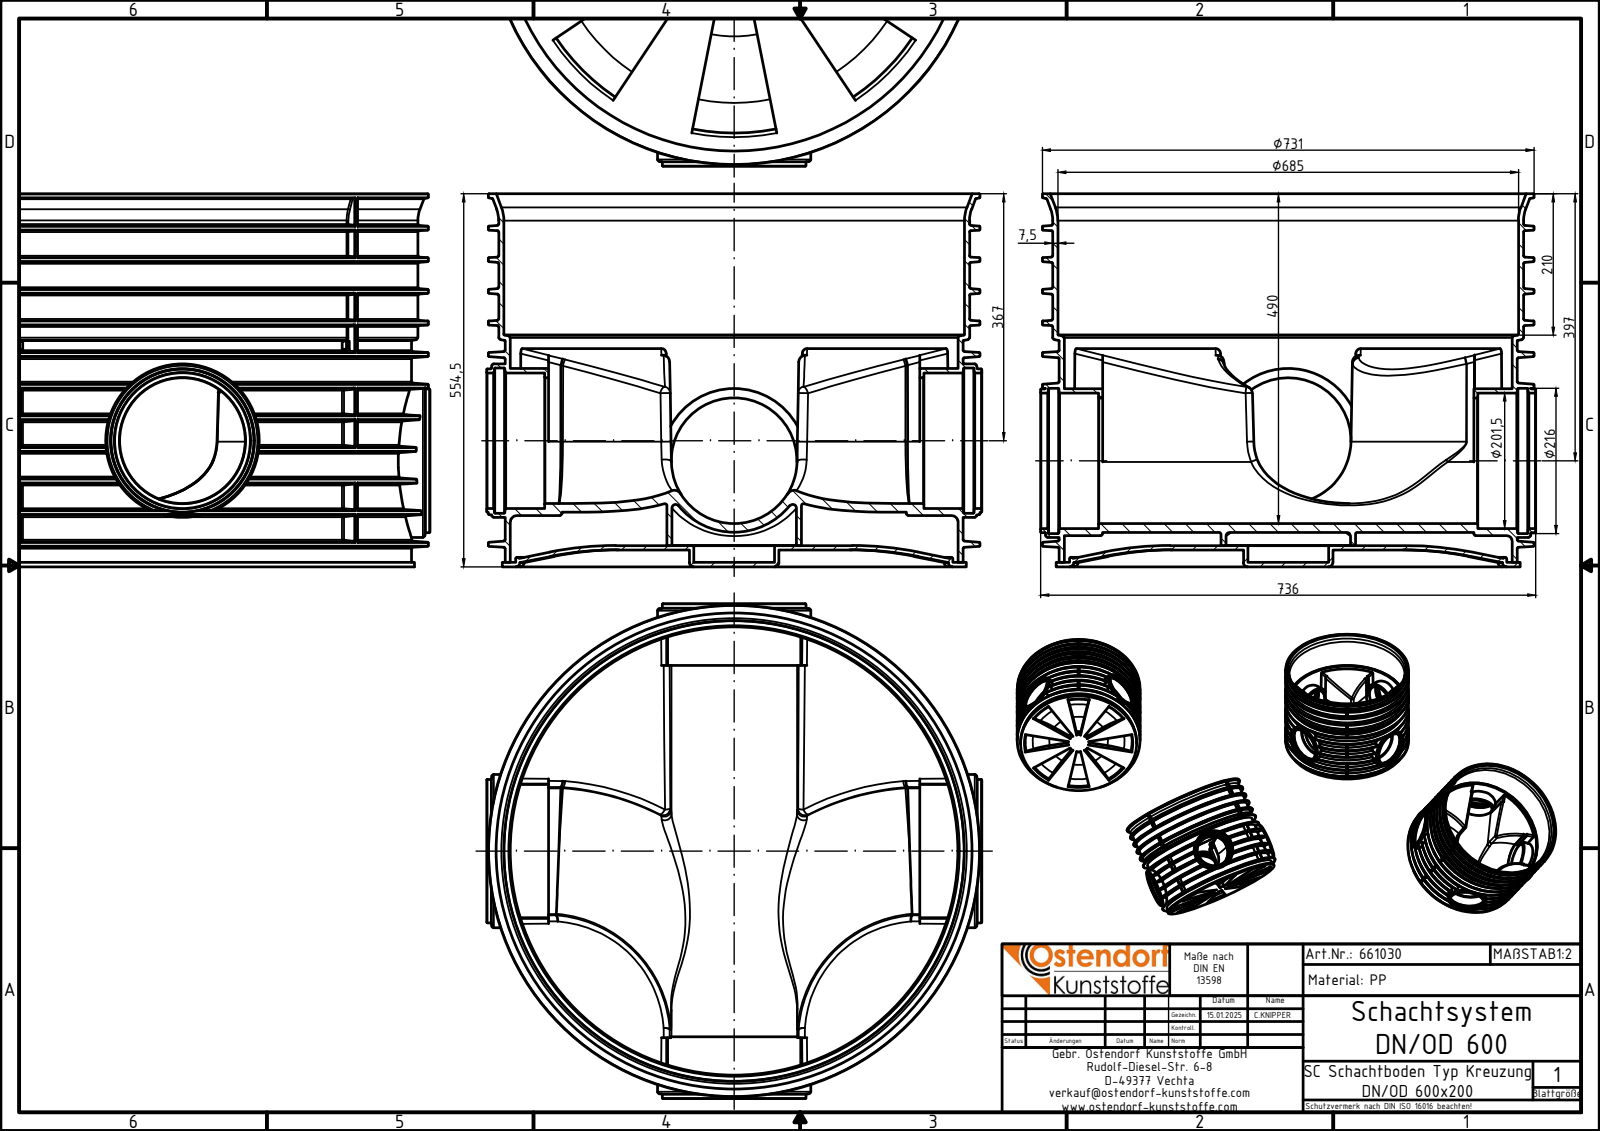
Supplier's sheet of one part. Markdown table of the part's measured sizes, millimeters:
| quantity | value |
| --- | --- |
| part name | 661030z; 661030 Schacht DN600 Boden; 661030 Schachtboden DN600 Grundkörper |
| STEP written by | Autodesk Inventor 2024 (AUTOMOTIVE_DESIGN) |
| units | millimeters |
| bodies | 2 solids, 1602 faces (198 planar, 287 cylindrical, 1117 other) |
| overall size | 736 × 736 × 554.5 |
| volume | 26 500 000 mm³ |
| surface area | 5 559 000 mm² |
| round holes (diameter × count) | 186.7 × 2, 201.5 × 2, 216 × 2, 120 × 1, 185 × 1, 640 × 1, 666 × 1, 685 × 1 |
| round bosses / shafts (diameter × count) | 228 × 2, 213.5 × 2, 731 × 1, 700 × 1, 690 × 1, 681 × 1, 650 × 1, 200 × 1 |
| partial cylindrical surfaces (radius × count) | 2 × 16, 1 × 8, 3 × 8, 106.35 × 3, 93.35 × 2, 107.25 × 2, 111.35 × 2, 66.5 × 1 |
| main face-to-face distances | 6.5, 25, 31.5, 13, 18.5, 5, 554.5, 548, 529.5, 523 |
